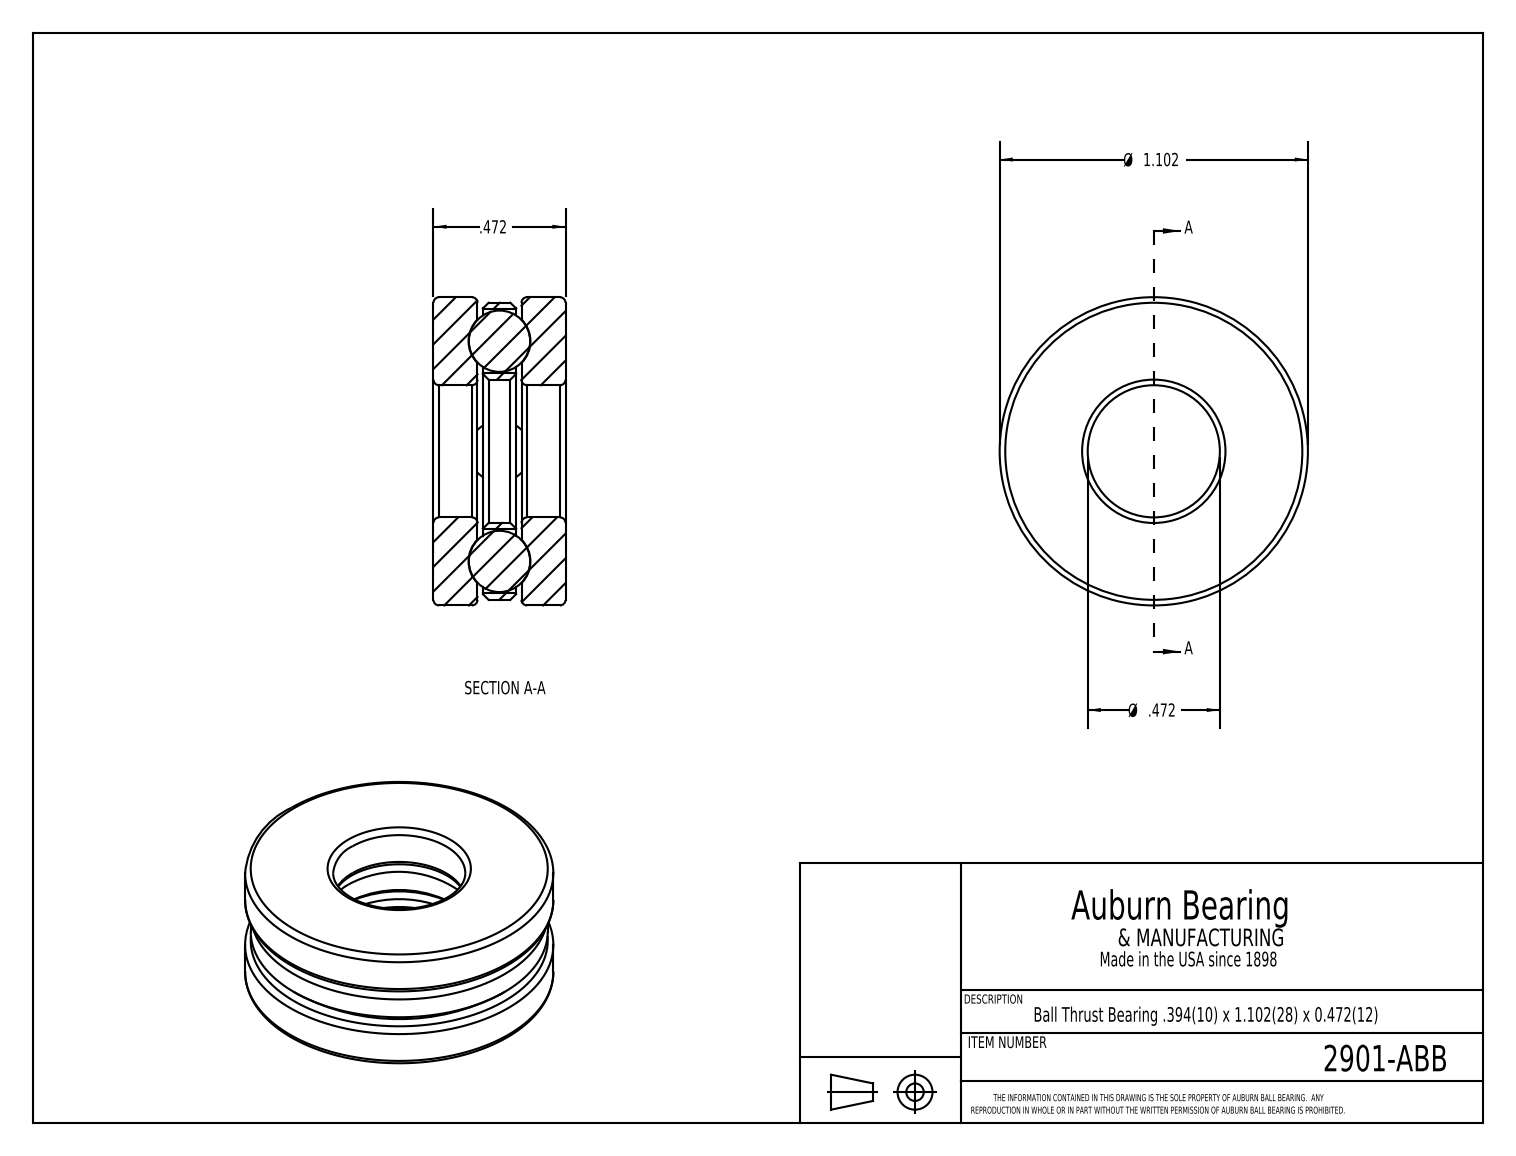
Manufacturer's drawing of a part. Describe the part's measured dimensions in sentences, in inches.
The part is named "2901". Its 3-D file was written by "SolidWorks 2017 (CONFIG_CONTROL_DESIGN)". It is 7 solids with 36 faces: 8 planar, 10 cylindrical and 18 other. Overall it measures 1.102 by 1.102 by 0.472 inches. Its volume is 0.307 cubic inches and its surface area 7.024 square inches. Round holes: 4 of diameter 0.229, 1 of diameter 0.472, 1 of diameter 0.512. Round bosses or shafts: 1 of diameter 1.102, 1 of diameter 1.062. The main face-to-face distances are 0.177, 0.295, 0.472, 0.157, 0.315, 0.02, 0.138, 0.118, 0.157. The hole center spacings are 0.394, 0.557, 0.787.
